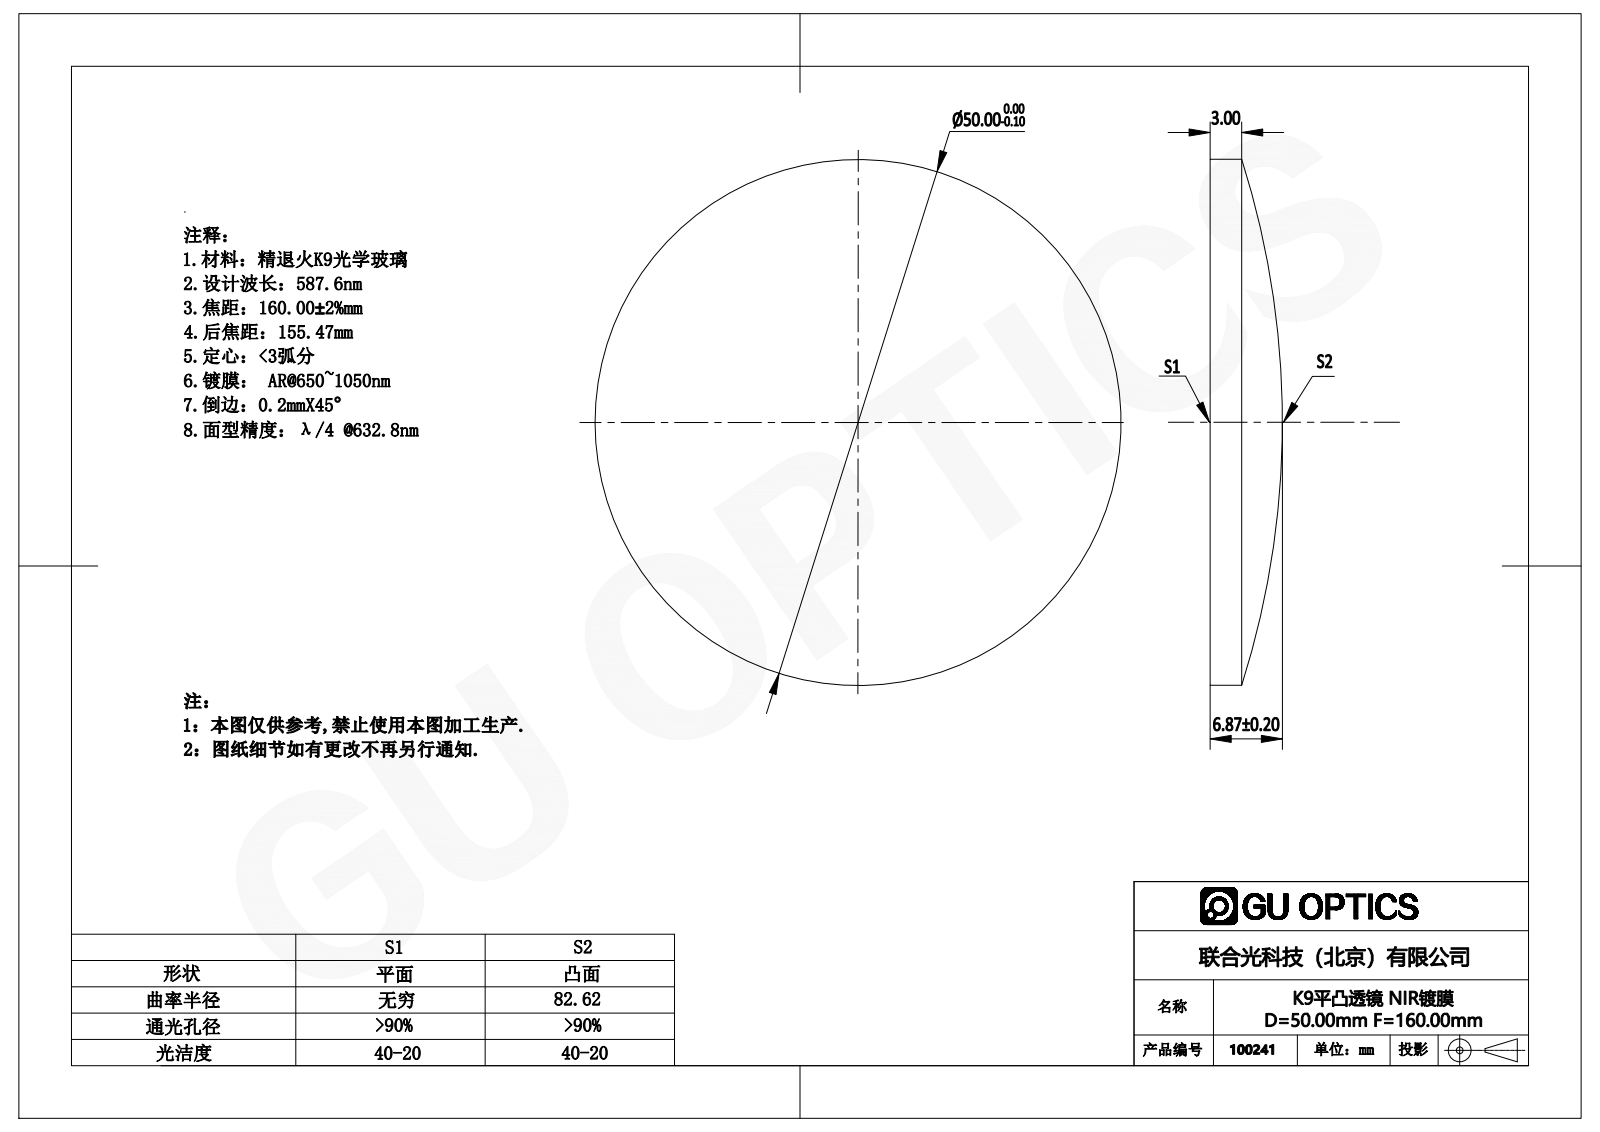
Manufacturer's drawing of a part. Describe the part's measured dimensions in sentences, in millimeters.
The part is named "100241". Its 3-D file was written by "SolidWorks 2016 (AUTOMOTIVE_DESIGN)". It is 1 solid with 5 faces: 1 planar, 2 cylindrical and 2 other. Overall it measures 50 by 50 by 6.87 millimeters. Its volume is 9 720 cubic millimeters and its surface area 4 445 square millimeters. Round bosses or shafts: 1 of diameter 50.
